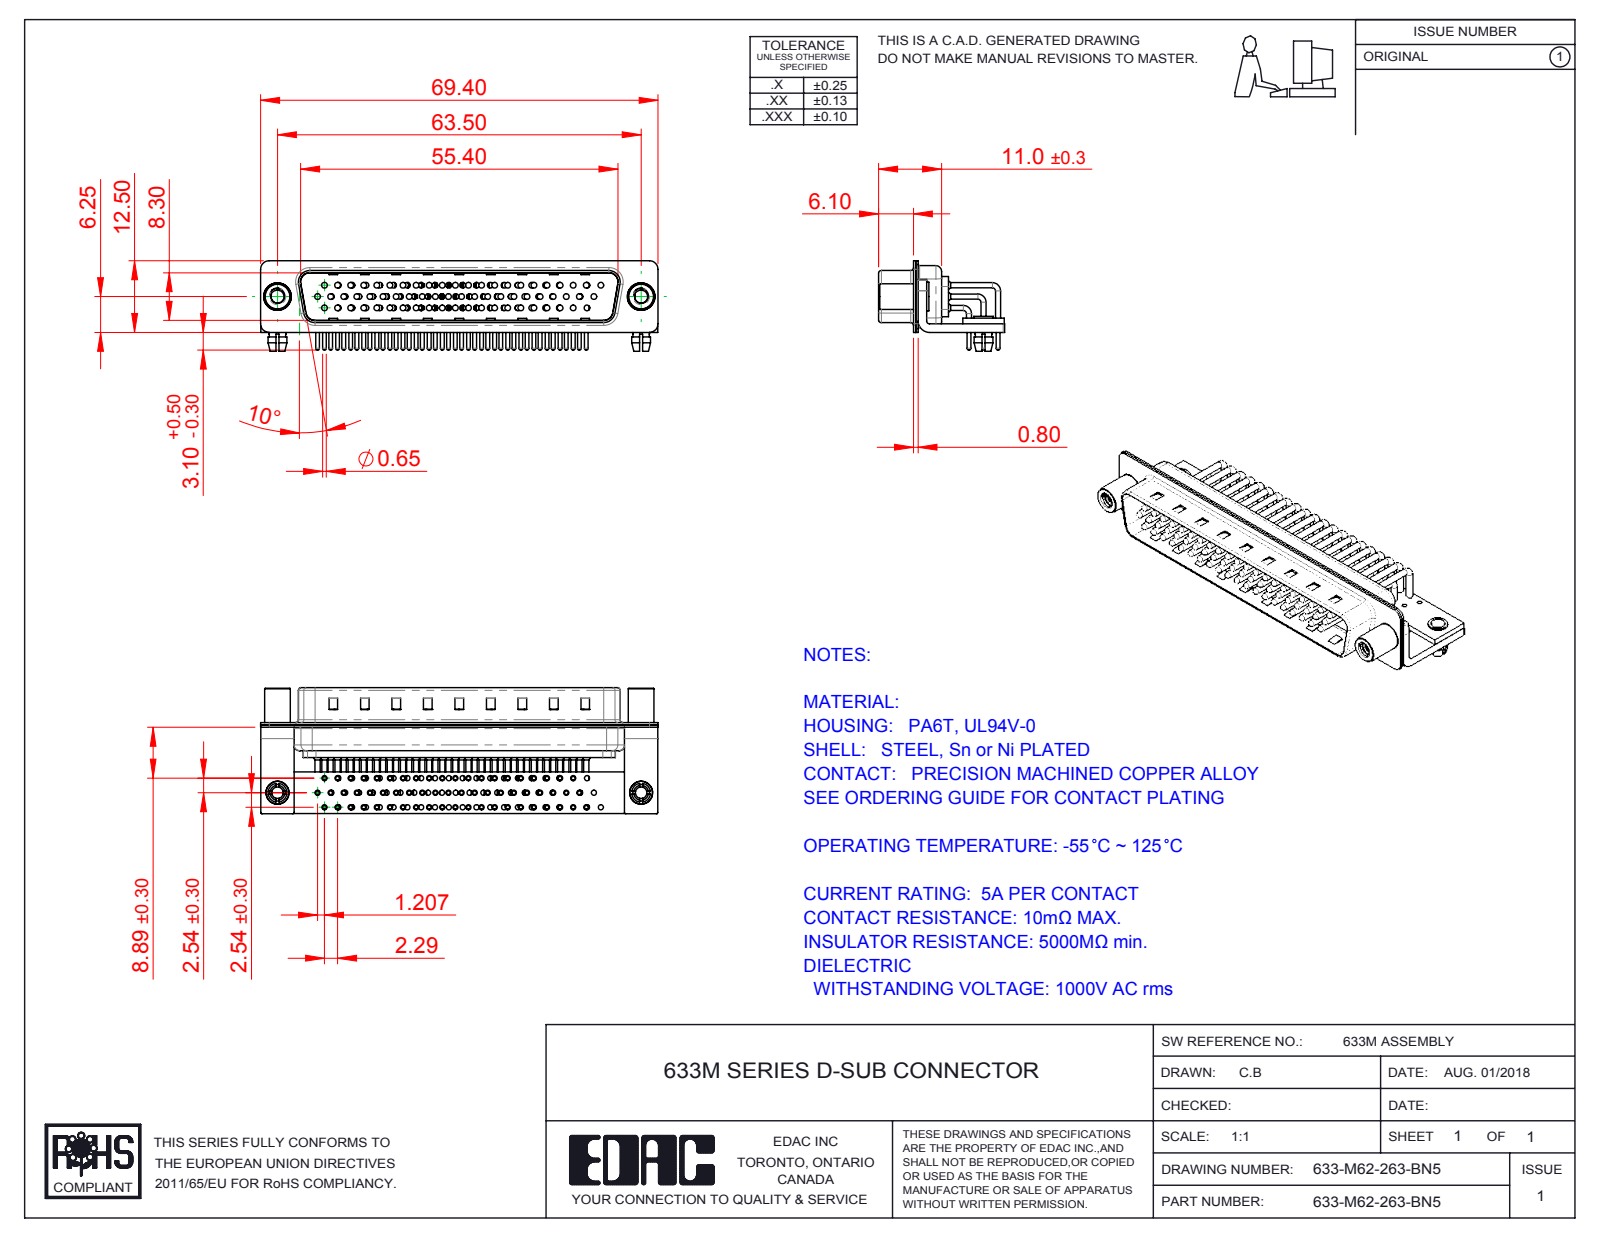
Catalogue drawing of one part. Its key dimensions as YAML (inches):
part_name: "633M Shell Front_62 Contacts; 633M Shell Rear_62 Contacts; 633M Contact Row 1; 633M Stabilizer Board_62 Contacts (+7 more)"
step_written_by: "SolidWorks 2016 (CONFIG_CONTROL_DESIGN)"
units: inches
bodies: {solids: 72, faces: 7548, planar: 4247, cylindrical: 2593, other: 708}
overall_size: [2.732, 0.866, 0.622]
volume: 0.32
surface_area: 24.9
round_holes:
  - {diameter: 0.079, count: 64}
  - {diameter: 0.035, count: 62}
  - {diameter: 0.039, count: 62}
  - {diameter: 0.067, count: 62}
  - {diameter: 0.089, count: 2}
  - {diameter: 0.098, count: 2}
  - {diameter: 0.126, count: 2}
  - {diameter: 0.157, count: 2}
  - {diameter: 0.189, count: 2}
round_bosses_or_shafts:
  - {diameter: 0.035, count: 118}
  - {diameter: 0.059, count: 62}
  - {diameter: 0.026, count: 62}
  - {diameter: 0.039, count: 56}
  - {diameter: 0.197, count: 2}
  - {diameter: 0.193, count: 2}
  - {diameter: 0.177, count: 2}
  - {diameter: 0.157, count: 2}
partial_cylinders:
  - {radius: 0.04, count: 62}
  - {radius: 0.01, count: 16}
  - {radius: 0.059, count: 16}
  - {radius: 0.079, count: 13}
  - {radius: 0.02, count: 9}
  - {radius: 0.063, count: 8}
  - {radius: 0.024, count: 4}
  - {radius: 0.026, count: 4}
face_to_face_distances: [0.016, 0.033, 0.049, 0.059, 0.376, 0.039, 0.075, 0.409, 0.327, 0.031]
hole_center_spacings: [0.285, 0.095, 0.38, 0.19, 0.57, 0.665, 0.111, 0.091]
